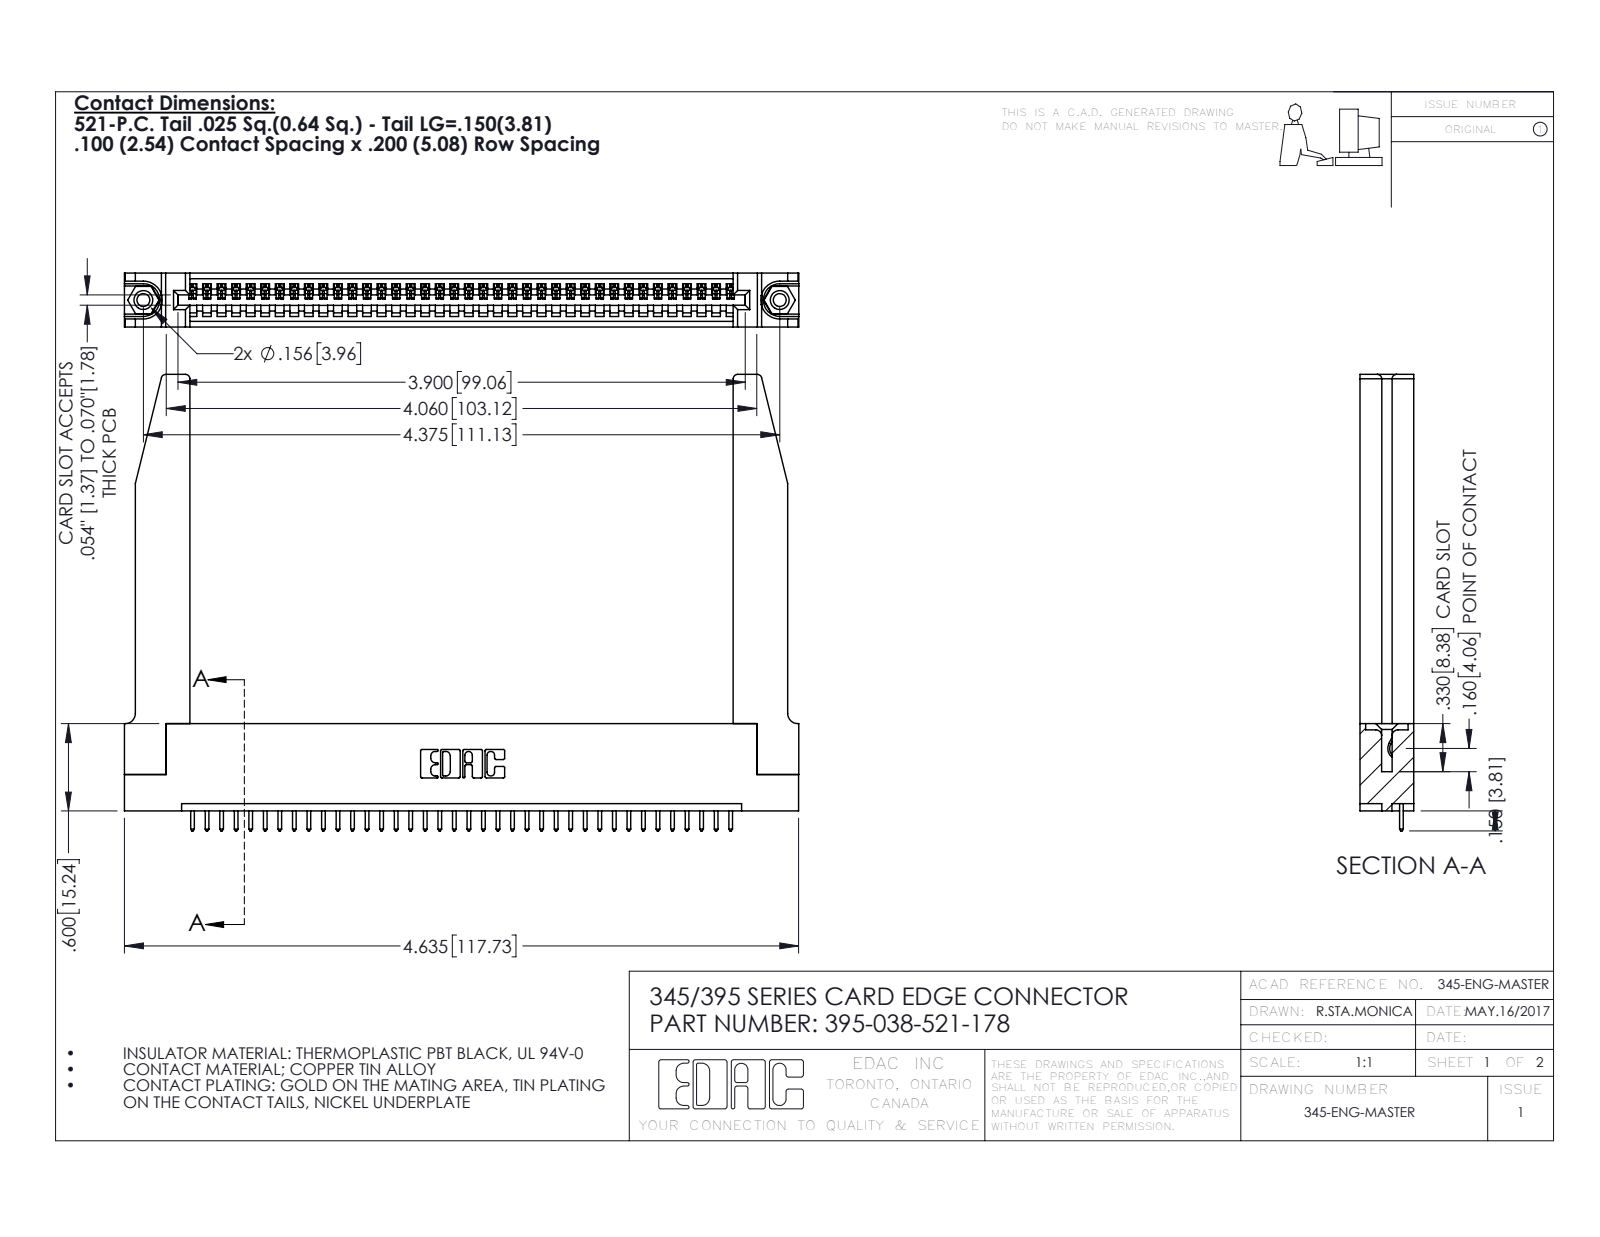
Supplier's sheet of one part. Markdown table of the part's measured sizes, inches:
| quantity | value |
| --- | --- |
| part name | 395-038-521-178; 345-220-078_345-220-078; 345-250-001_345-250-001-102; 345-292-001_345-293-121 (+1 more) |
| STEP written by | SolidWorks 2016 (CONFIG_CONTROL_DESIGN) |
| units | inches |
| bodies | 43 solids, 2564 faces (1742 planar, 770 cylindrical, 52 other) |
| overall size | 4.636 × 3.137 × 0.37 |
| volume | 1.148 in³ |
| surface area | 32.62 in² |
| round holes (diameter × count) | 0.089 × 2, 0.125 × 2, 0.156 × 2, 0.064 × 1 |
| round bosses / shafts (diameter × count) | 0.155 × 2 |
| partial cylindrical surfaces (radius × count) | 0.006 × 76, 0.01 × 76, 0.01 × 22, 0.03 × 8, 0.007 × 6, 0.031 × 6, 0.026 × 3, 0.031 × 2 |
| main face-to-face distances | 0.37, 0.072, 0.298, 0.2, 0.098, 0.272, 0.025, 0.225, 0.148, 0.15 |
| hole center spacings | 0.27, 4.139, 4.375 |
